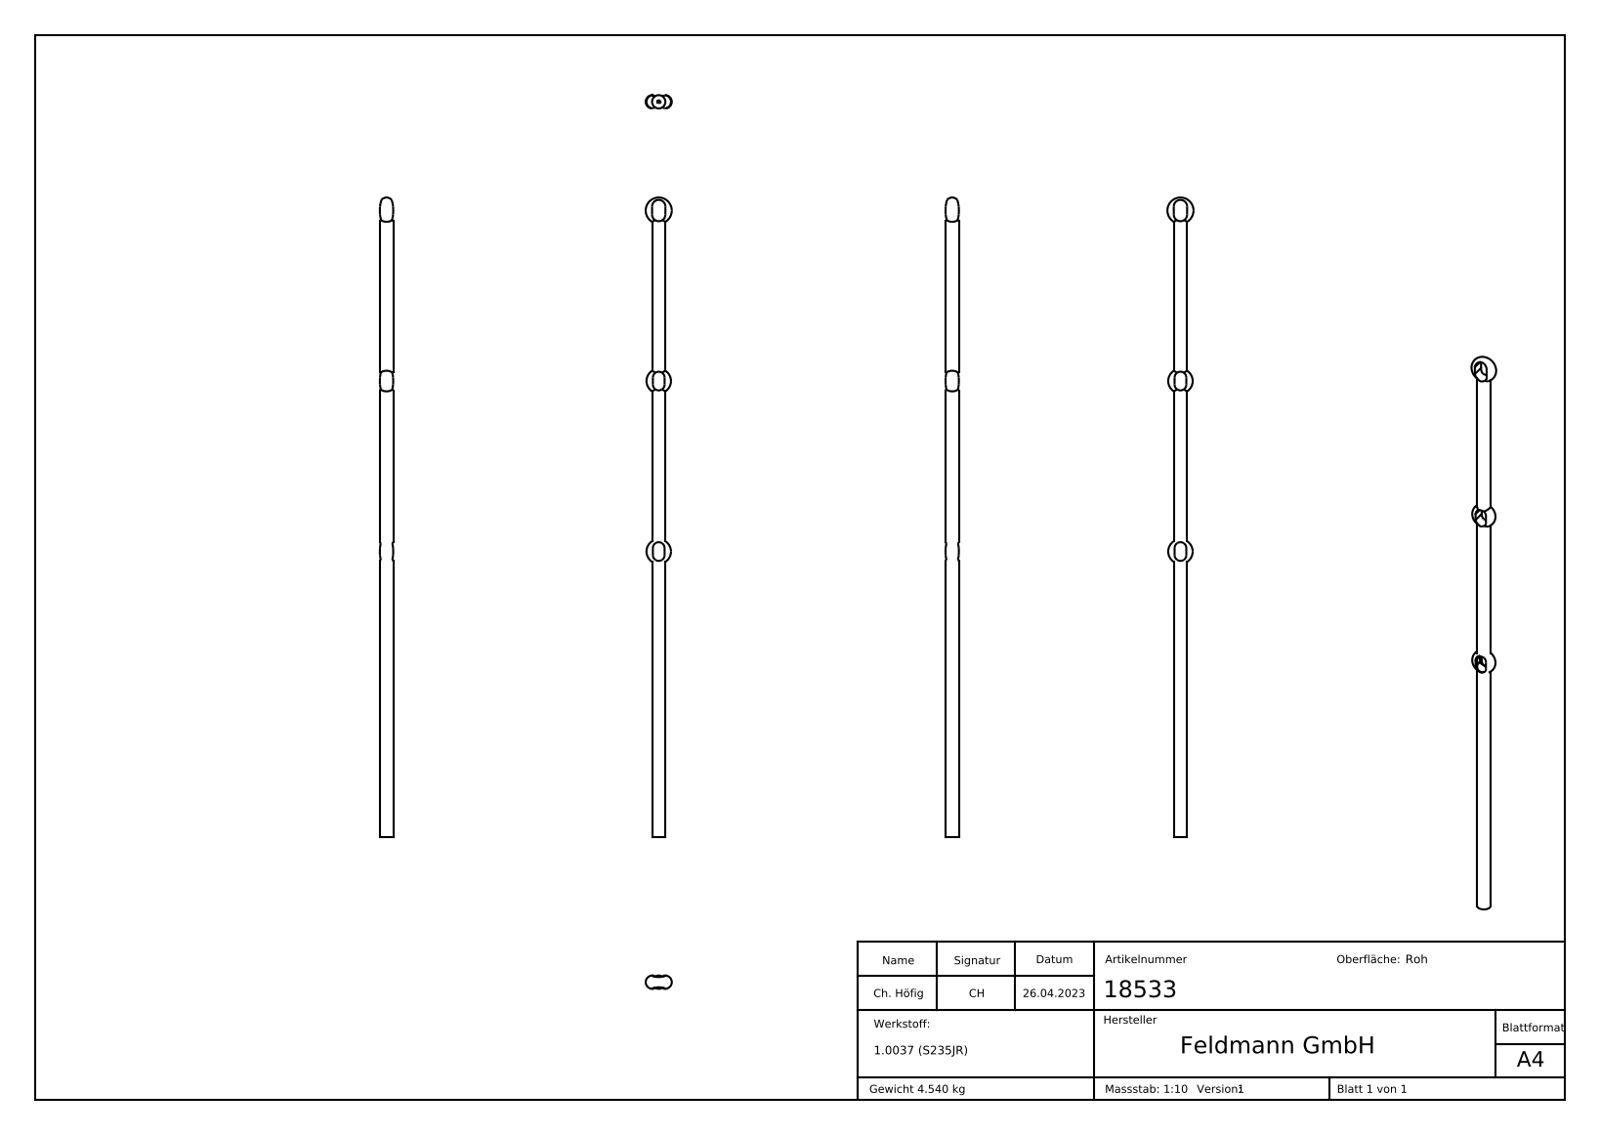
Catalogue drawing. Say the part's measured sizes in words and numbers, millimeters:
The part is named "18533". Its 3-D file was written by "SolidWorks 2018 (CONFIG_CONTROL_DESIGN)". It is 2 solids with 214 faces: 99 planar, 10 cylindrical and 105 other. Overall it measures 1200 by 49 by 25 millimeters. Its volume is 582 104 cubic millimeters and its surface area 105 727 square millimeters. Round bosses or shafts: 1 of diameter 25. Partial cylindrical surfaces (rounded edges, fillets, slot ends): 4 of radius 11, 2 of radius 12.5. The main face-to-face distances are 22, 1.5, 23.5, 25, 0.5, 1.78, 0.83, 1.21, 1.32, 11.25.
